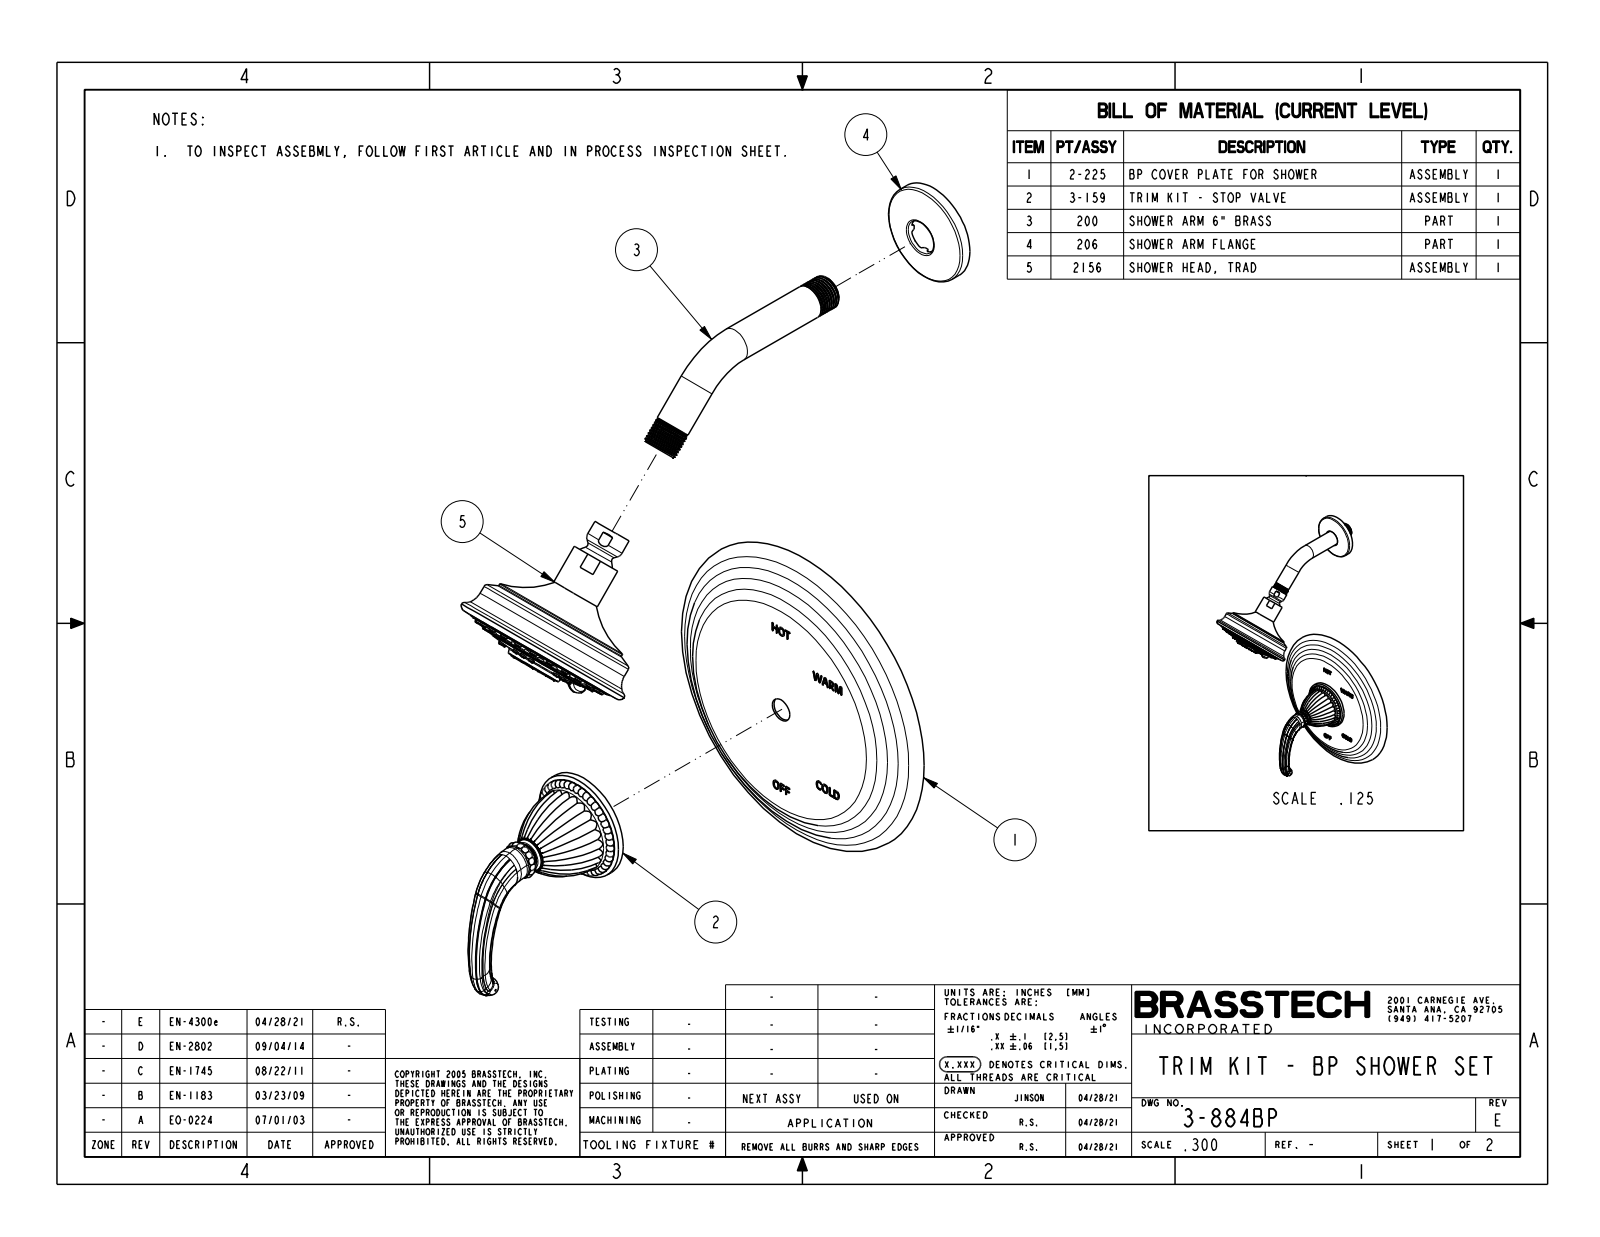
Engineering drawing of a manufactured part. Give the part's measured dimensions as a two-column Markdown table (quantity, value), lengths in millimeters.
| quantity | value |
| --- | --- |
| part name | 3-884BP |
| STEP written by | CREO PARAMETRIC BY PTC INC, 2018400 (CONFIG_CONTROL_DESIGN) |
| units | millimeters |
| bodies | 2 solids, 1822 faces (282 planar, 202 cylindrical, 1338 other) |
| overall size | 408.1 × 209.6 × 196.9 |
| volume | 875 100 mm³ |
| surface area | 124 800 mm² |
| round holes (diameter × count) | 1.5 × 8, 23.5 × 1 |
| round bosses / shafts (diameter × count) | 3.6 × 39, 4.2 × 23, 20.7 × 2, 96.8 × 1, 94.6 × 1, 82.3 × 1, 65.3 × 1, 60.5 × 1 |
| partial cylindrical surfaces (radius × count) | 2 × 8, 0.5 × 2, 3.5 × 1, 12 × 1, 13 × 1, 16 × 1 |
| main face-to-face distances | 19.2, 1.6, 3, 4.6, 73.2, 70.2, 68.6, 19.1, 65.1, 46.1 |
| hole center spacings | 11.3, 14.7, 27.2, 20.8, 20.8, 29.4, 29.4 |
